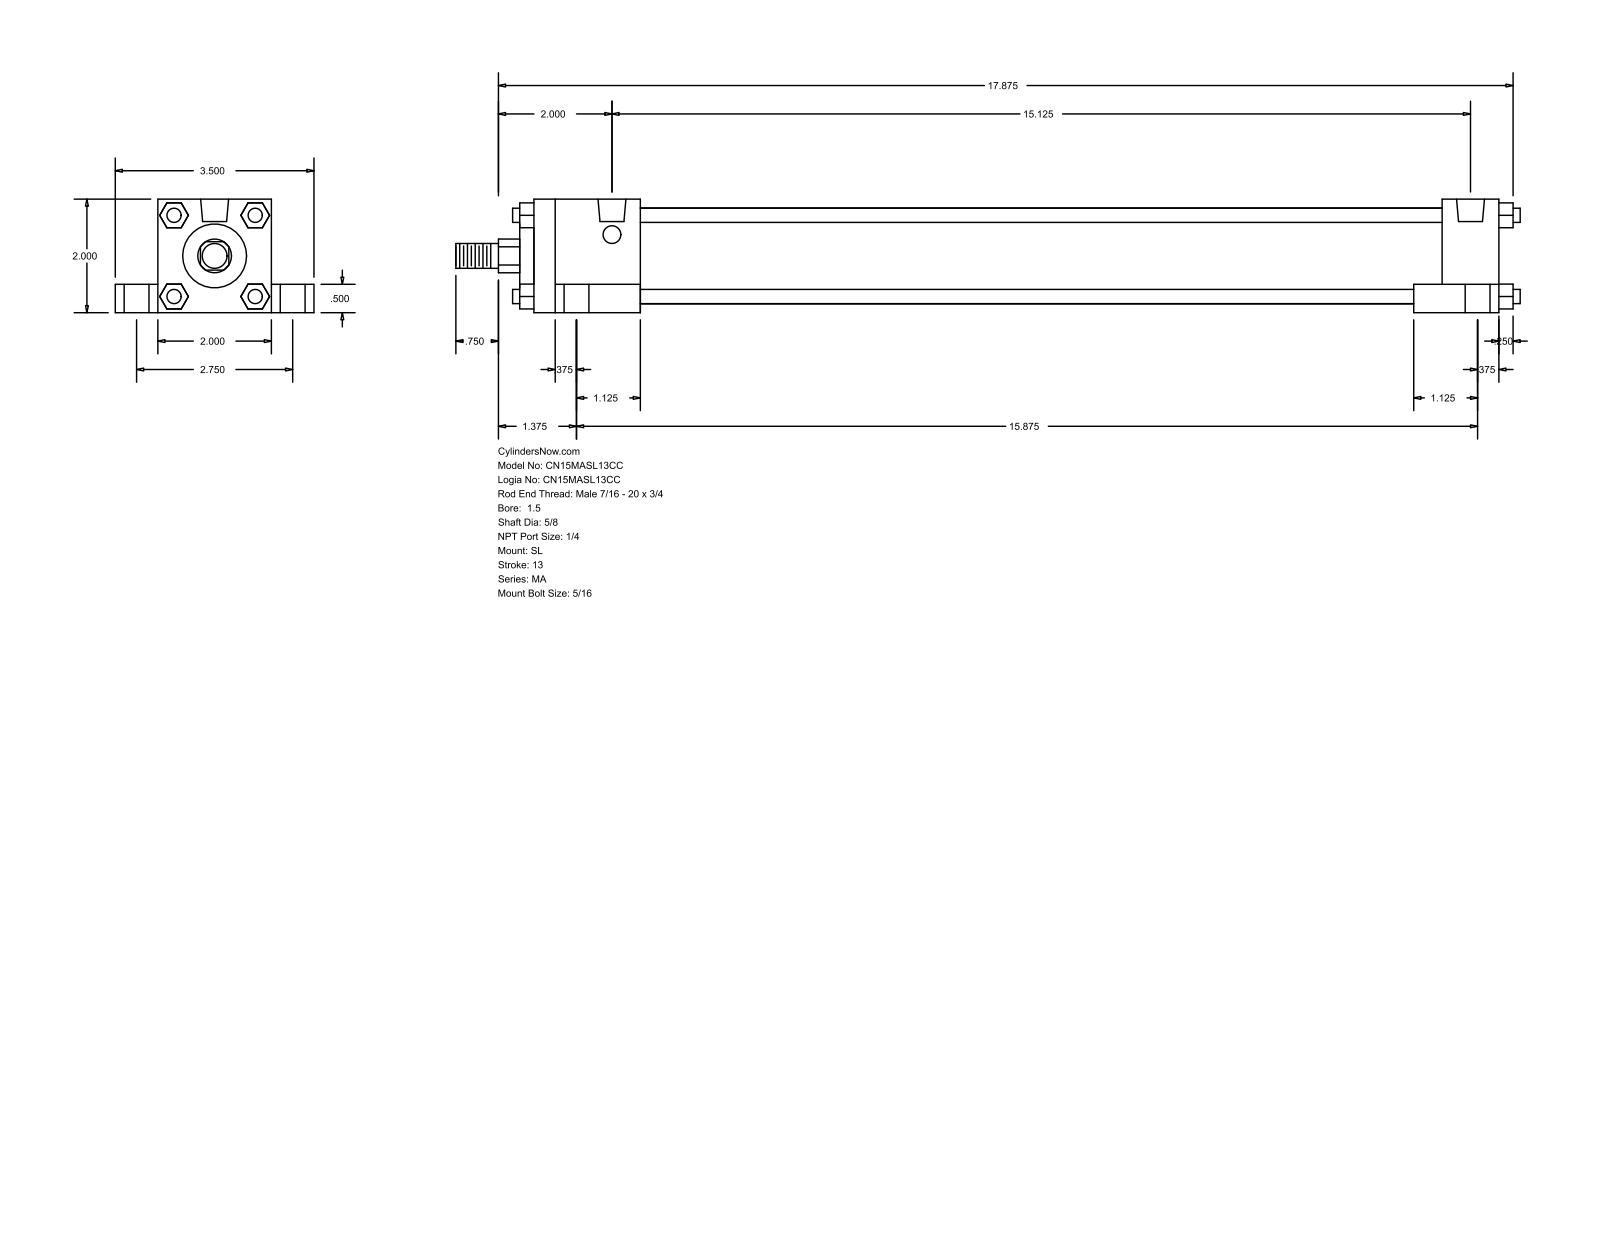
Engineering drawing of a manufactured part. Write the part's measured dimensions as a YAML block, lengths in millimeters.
part_name: "MA_SL__0150_0.625"
step_written_by: "GSSL Pune (CONFIG_CONTROL_DESIGN)"
units: millimeters
bodies: {solids: 0, faces: 148, planar: 112, cylindrical: 36, other: 0}
overall_size: [476.25, 88.9, 50.8]
round_holes:
  - {diameter: 7.94, count: 4}
  - {diameter: 11.11, count: 4}
  - {diameter: 17.46, count: 4}
  - {diameter: 12.49, count: 2}
round_bosses_or_shafts:
  - {diameter: 6.35, count: 4}
  - {diameter: 42.93, count: 1}
  - {diameter: 28.57, count: 1}
  - {diameter: 15.88, count: 1}
  - {diameter: 11.11, count: 1}
partial_cylinders:
  - {radius: 7.54, count: 1}
face_to_face_distances: [50.8, 19.05, 38.1, 431.8, 69.85, 12.7, 358.77, 9.52, 406.39, 25.41]
hole_center_spacings: [35.06, 38.36, 69.84, 384.18, 388.92, 401.58, 403.23, 409.23]
